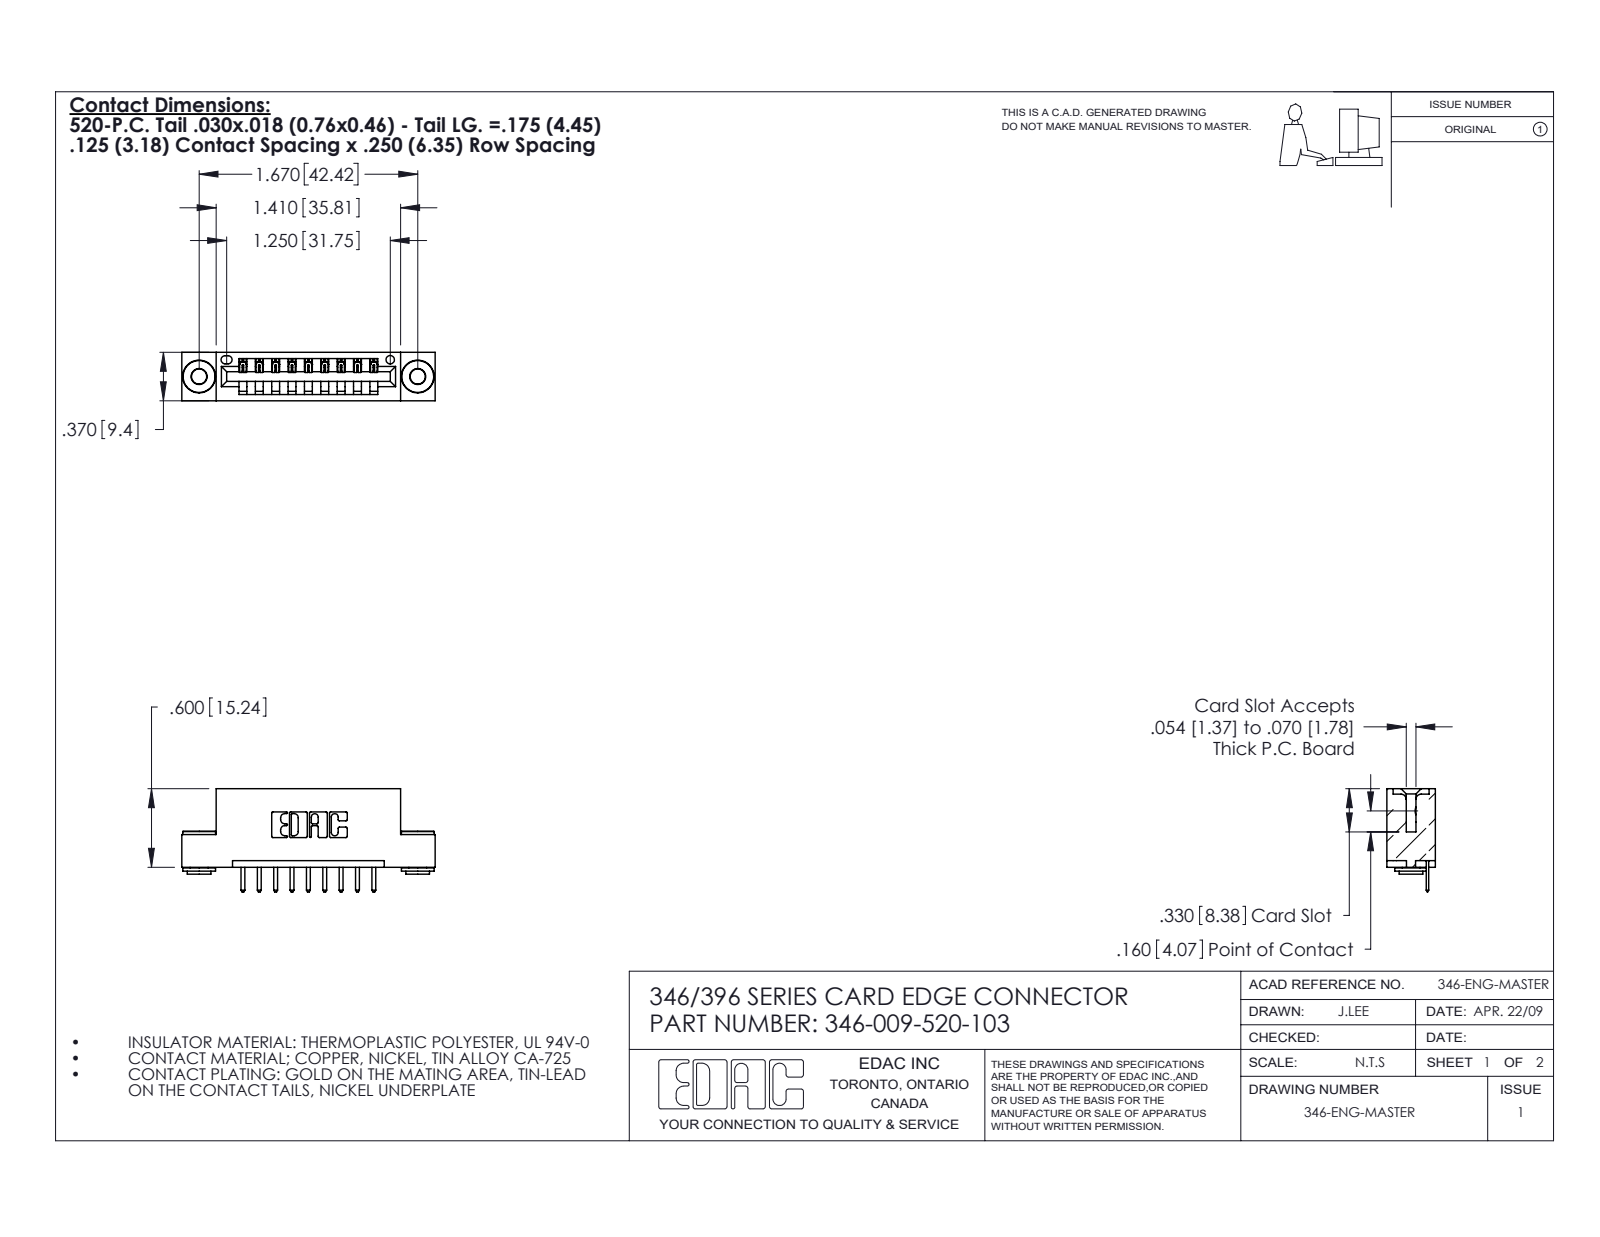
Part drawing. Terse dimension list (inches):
name: 346 Part_Flush Mounting Lugs - 0.156 Dia-TH; 346-009-520-103; 345-250-002_345-250-002-102; 345-292-001_345-293-120
written by: SolidWorks 2020 (CONFIG_CONTROL_DESIGN)
unit: in
bodies: 12 solids, 732 faces (478 planar, 246 cylindrical, 8 other)
size: 1.935 × 0.788 × 0.37
volume: 0.272 in³; area: 8.33 in²
holes: 2× ⌀0.116, 2× ⌀0.156, 1× ⌀0.064
bosses: 2× ⌀0.25, 2× ⌀0.18, 2× ⌀0.136
rounds: 22× R0.01, 20× R0.01, 18× R0.006, 6× R0.007, 6× R0.031, 3× R0.026, 2× R0.031, 2× R0.04
face distances: 0.25, 0.37, 0.048, 0.322, 0.148, 0.222, 0.1, 0.174, 0.025, 0.125
hole spacings: 0.246, 1.465, 1.67
